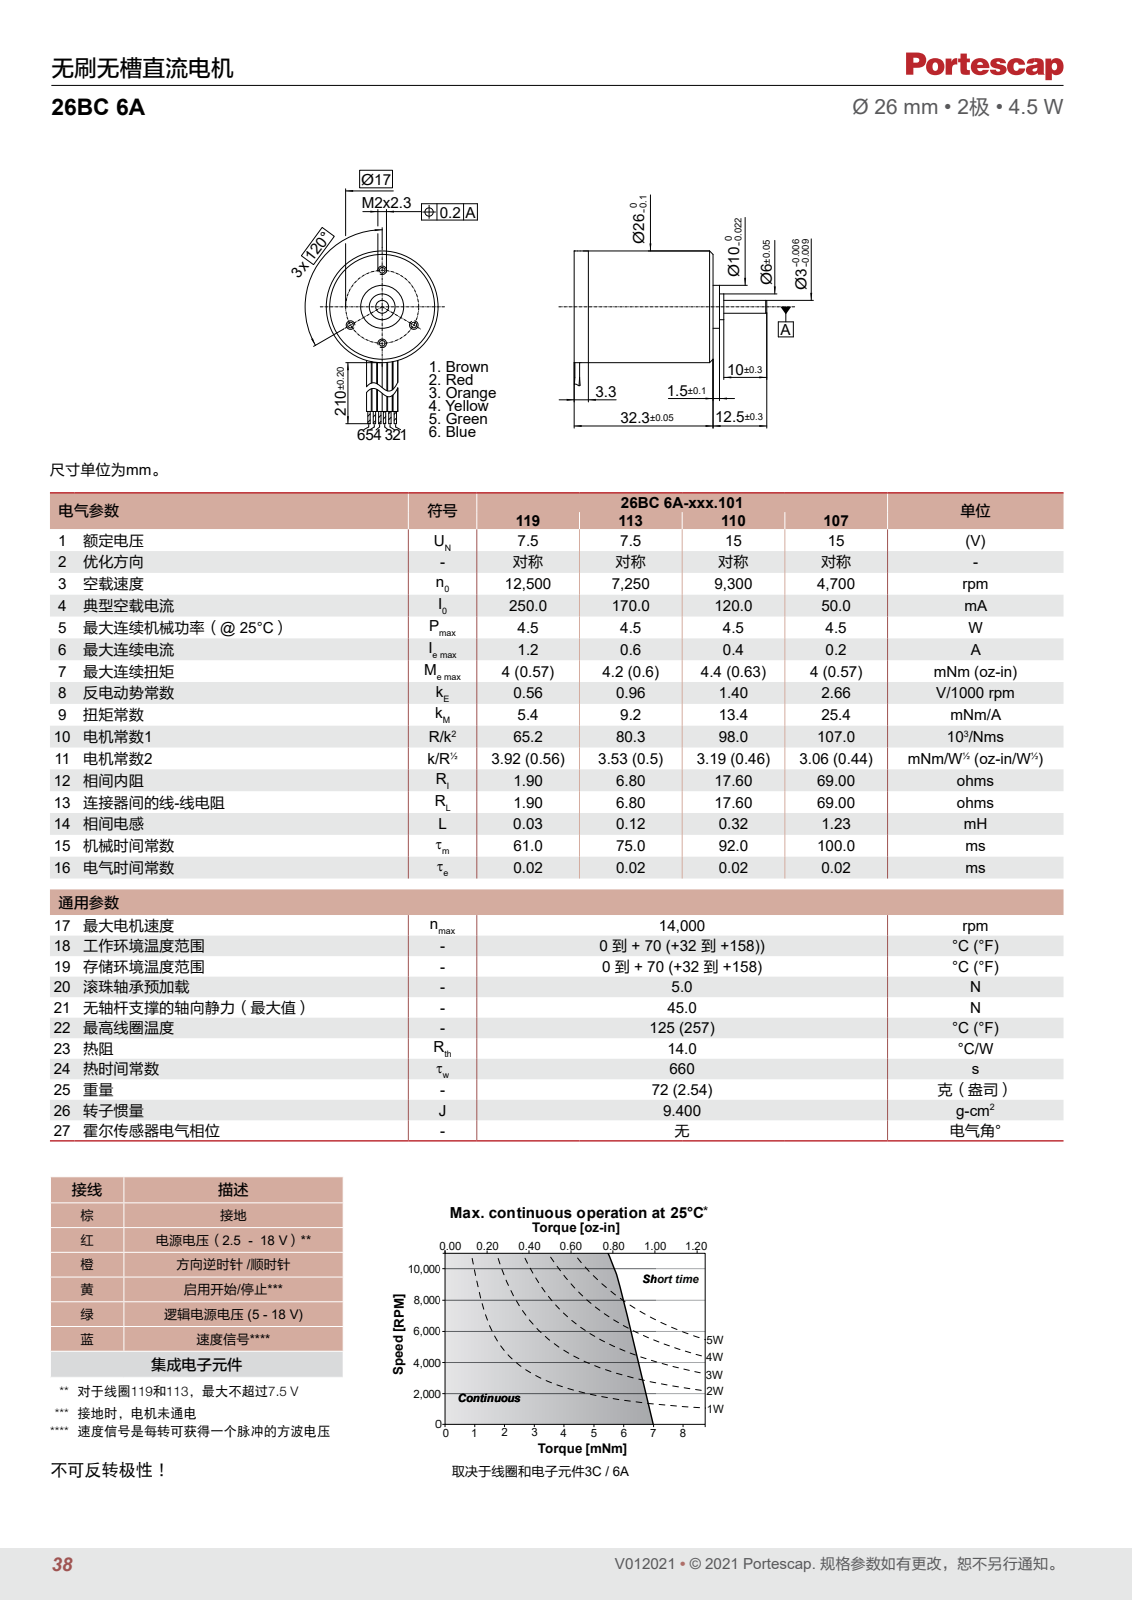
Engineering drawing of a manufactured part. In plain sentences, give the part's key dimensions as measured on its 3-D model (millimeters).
The part is named "26BC_6A_ASM". Its 3-D file was written by "PRO/ENGINEER BY PARAMETRIC TECHNOLOGY CORPORATION, 2014310 (CONFIG_CONTROL_DESIGN)". It is 7 solids with 253 faces: 61 planar, 123 cylindrical and 69 other. Overall it measures 76.09 by 44.8 by 26 millimeters. Its volume is 17 318 cubic millimeters and its surface area 4 912 square millimeters. Round holes: 13 of diameter 2, 4 of diameter 1.6, 3 of diameter 1.5, 1 of diameter 6, 1 of diameter 8. Round bosses or shafts: 12 of diameter 1, 6 of diameter 0.8, 6 of diameter 0.4, 1 of diameter 26, 1 of diameter 10, 1 of diameter 3. Partial cylindrical surfaces (rounded edges, fillets, slot ends): 6 of radius 2, 1 of radius 0.5. The main face-to-face distances are 32.3, 1.5, 33.8, 32.7, 31.2, 1.1, 2.5, 0.7, 31.5, 33.1. The hole center spacings are 7.7, 8.5, 16.44, 3.97, 11.25, 11.68, 13.33, 1.95.
